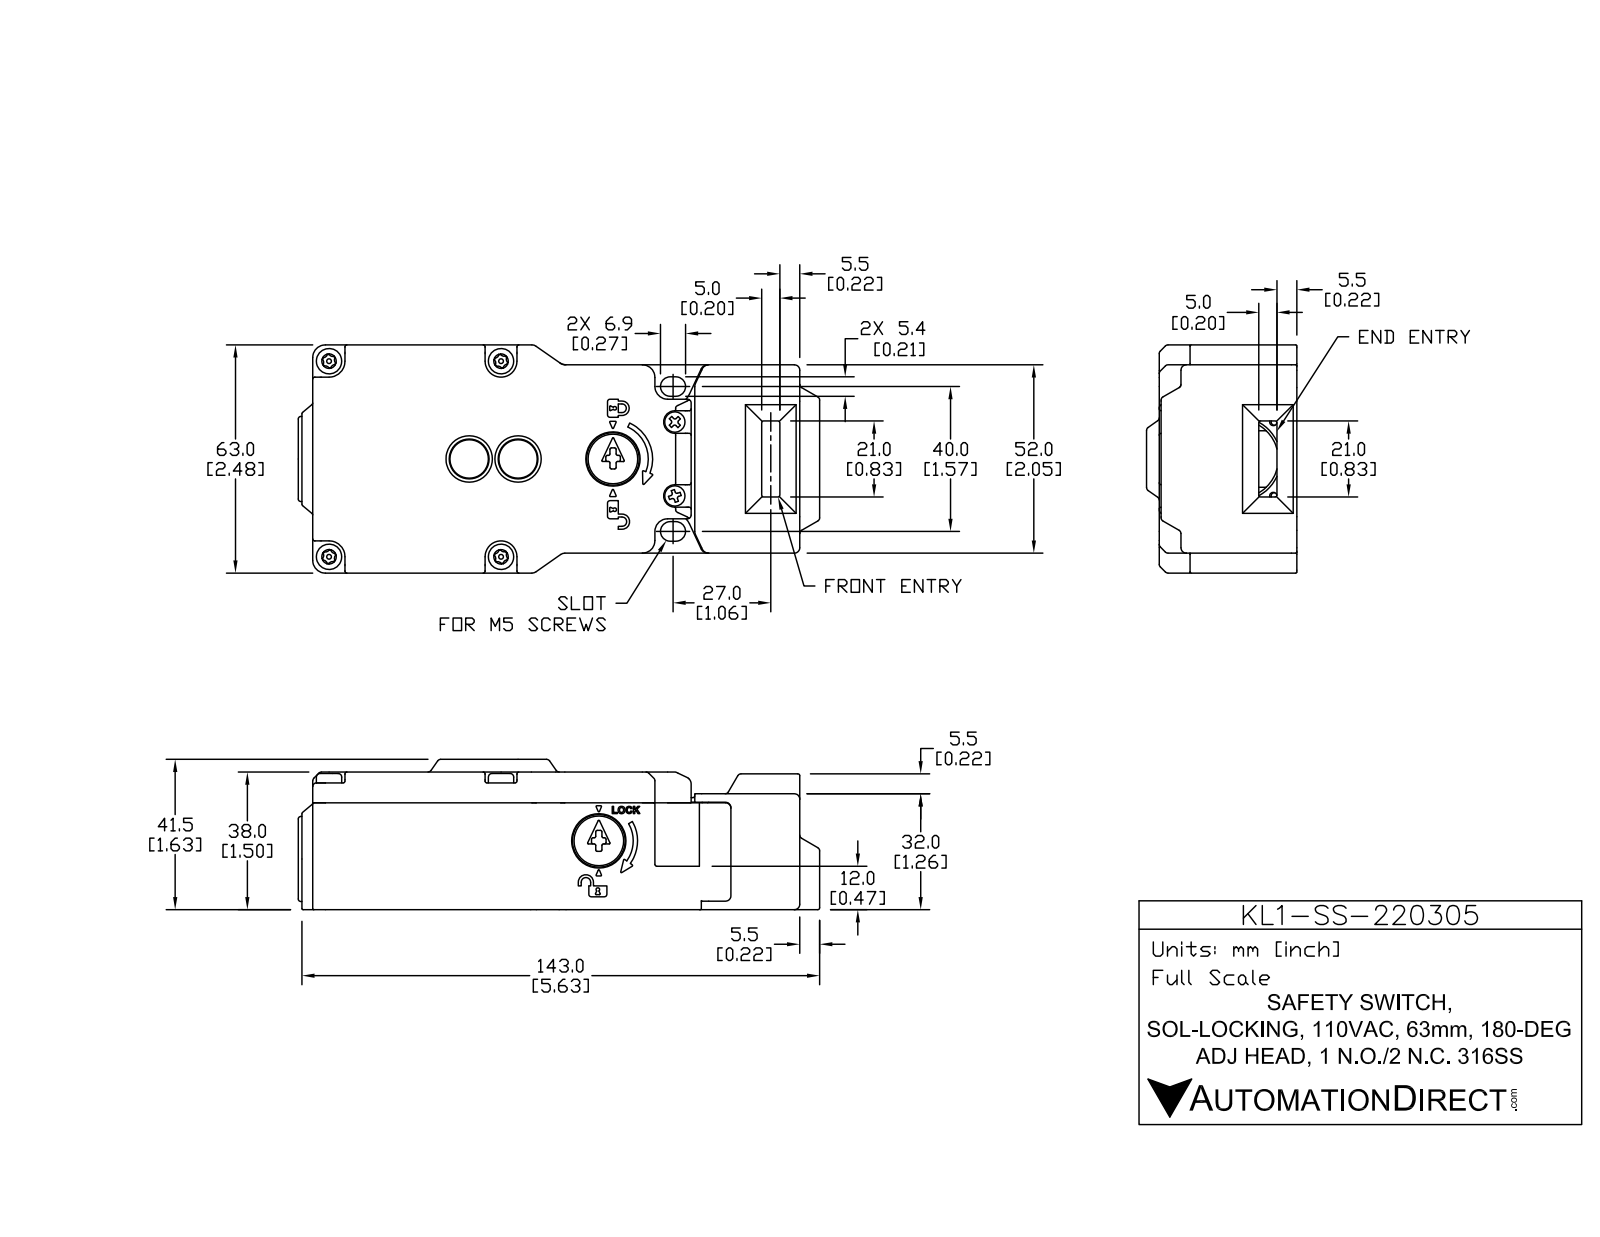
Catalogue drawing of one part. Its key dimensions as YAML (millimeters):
part_name: "KL1-SS-220305"
step_written_by: "SolidWorks 2017 (AUTOMOTIVE_DESIGN)"
units: millimeters
bodies: {solids: 18, faces: 3047, planar: 909, cylindrical: 1225, other: 913}
overall_size: [144, 63, 41.5]
volume: 104000
surface_area: 76650
round_holes:
  - {diameter: 2.6, count: 4}
  - {diameter: 3.4, count: 4}
  - {diameter: 4, count: 4}
  - {diameter: 4.1, count: 4}
  - {diameter: 4.5, count: 4}
  - {diameter: 5, count: 4}
  - {diameter: 2, count: 2}
  - {diameter: 2.1, count: 2}
  - {diameter: 3, count: 2}
  - {diameter: 3.2, count: 2}
  - {diameter: 3.6, count: 2}
  - {diameter: 6.7, count: 2}
round_bosses_or_shafts:
  - {diameter: 7, count: 4}
  - {diameter: 3.5, count: 4}
  - {diameter: 1.3, count: 4}
  - {diameter: 5, count: 3}
  - {diameter: 1, count: 3}
  - {diameter: 14.5, count: 2}
  - {diameter: 10.6, count: 2}
  - {diameter: 9.2, count: 2}
partial_cylinders:
  - {radius: 0.5, count: 348}
  - {radius: 0.3, count: 126}
  - {radius: 1, count: 106}
  - {radius: 0.2, count: 30}
  - {radius: 0.4, count: 24}
  - {radius: 1.5, count: 16}
  - {radius: 0.2, count: 14}
  - {radius: 0.7, count: 12}
face_to_face_distances: [2.5, 3, 5.5, 38, 35.5, 35.6, 33.1, 2.4, 57.5, 54.5]
hole_center_spacings: [10.3, 12.6, 13.1, 13.9, 19.9, 20.4, 27.4, 28.4]
